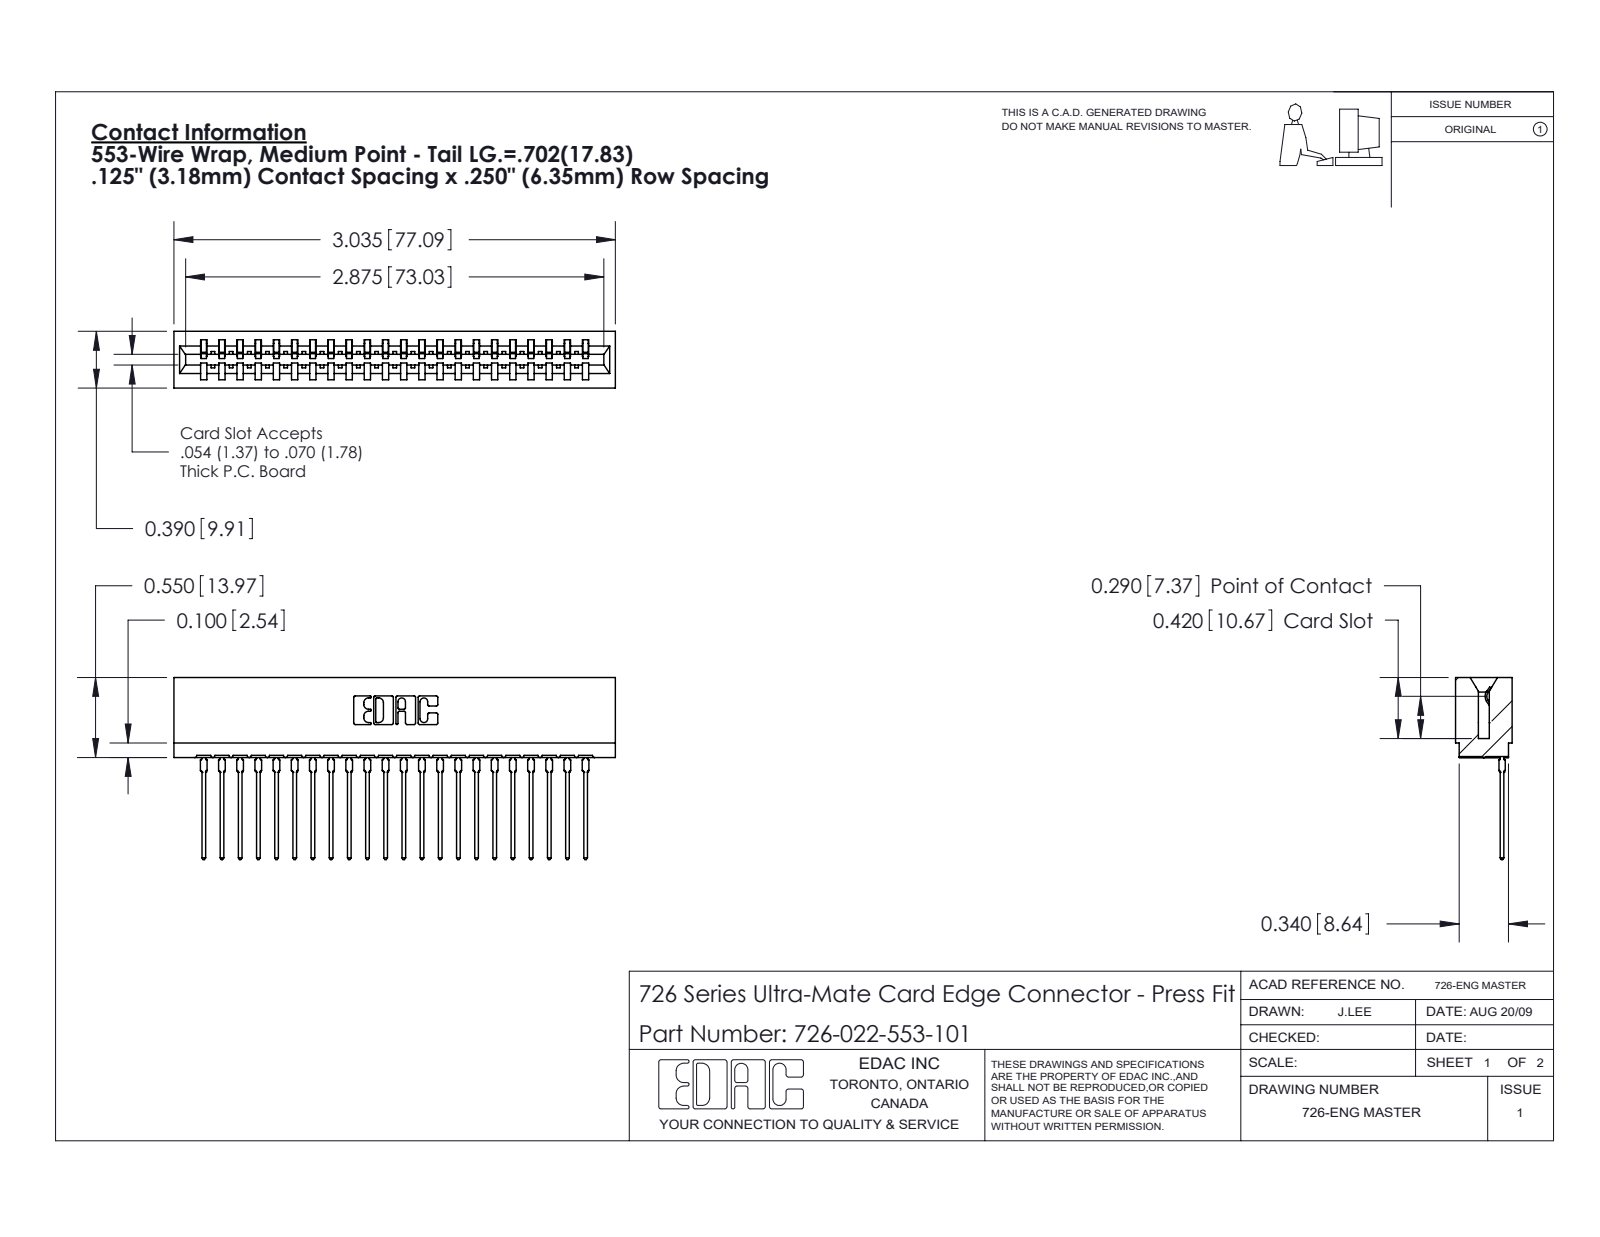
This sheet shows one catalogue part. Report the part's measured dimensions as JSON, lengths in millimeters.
{"part_name": "726-022-553-101; 746-292-001_553; 726 Part_.515 Slot Depth - 01", "step_written_by": "SolidWorks 2020 (CONFIG_CONTROL_DESIGN)", "units": "millimeters", "bodies": {"solids": 23, "faces": 2473, "planar": 1441, "cylindrical": 460, "other": 572}, "overall_size": [77.1, 31.8, 9.9], "volume_mm3": 7080, "surface_area_mm2": 10920, "partial_cylinders_radius": [[0.5, 44], [0.4, 23], [0.3, 22], [0.2, 6], [0.8, 6], [0.1, 4], [0.3, 4], [0.7, 3]], "face_to_face_distances": [1.4, 8.5, 9.9, 0.6, 7.8, 6.4, 2.1, 1.1, 31.8, 3.2]}
